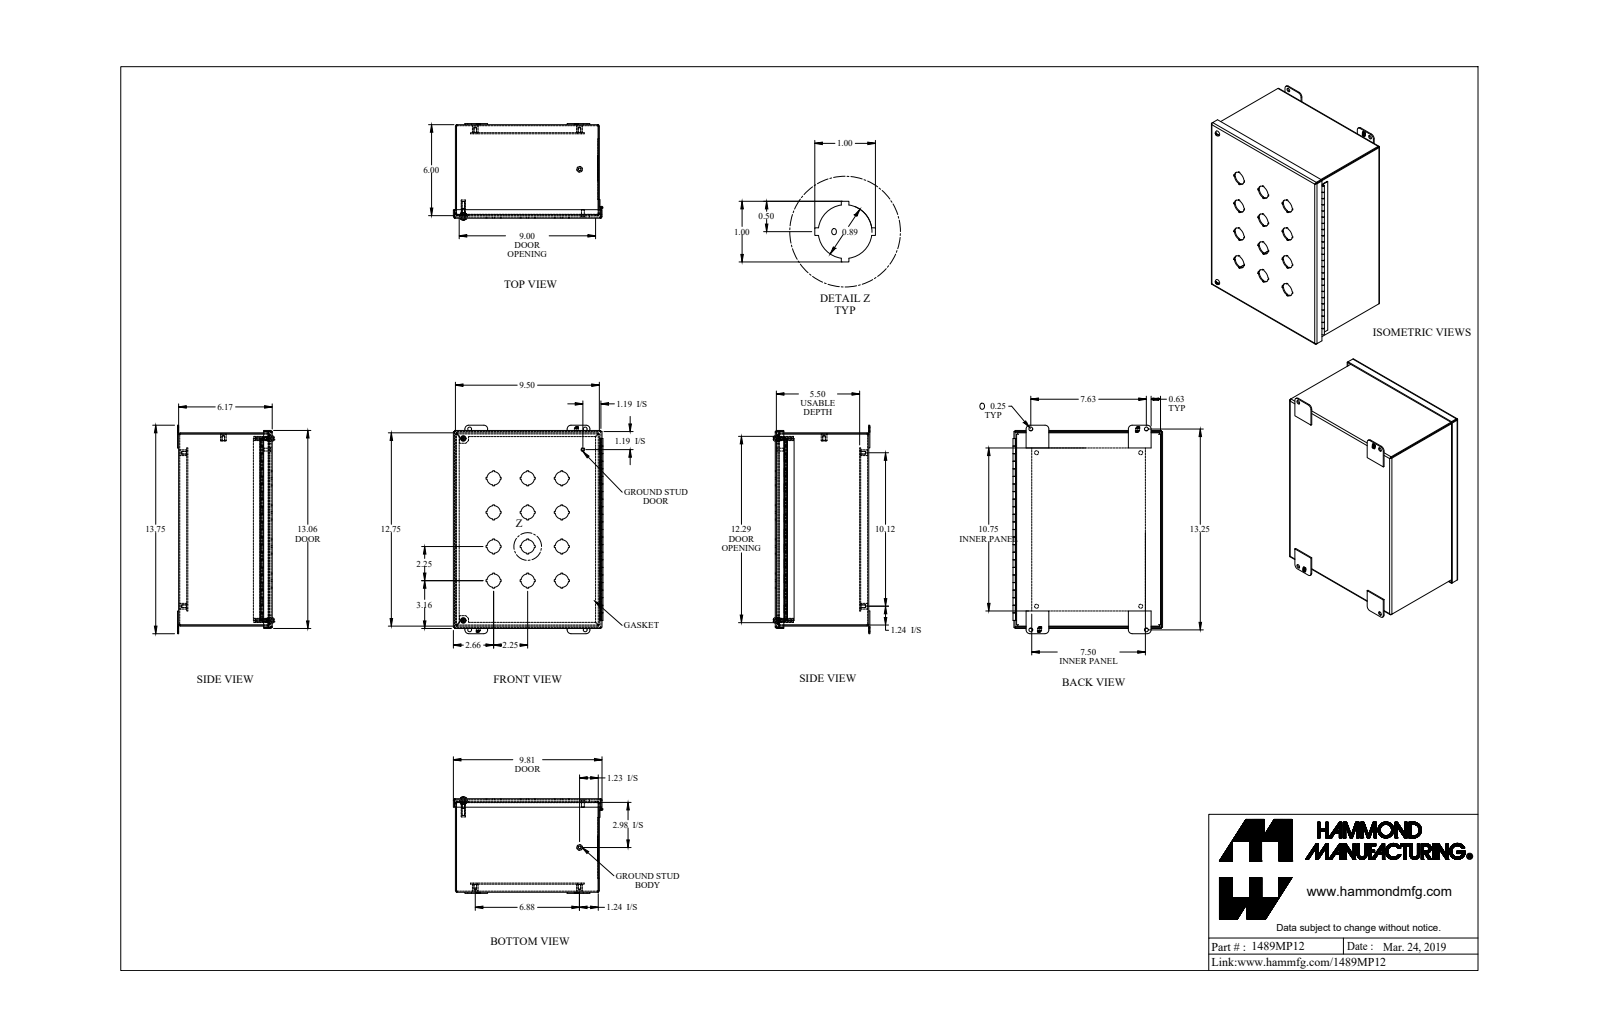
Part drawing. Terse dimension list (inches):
name: 1489MP12_Default
written by: SolidWorks 2019 (CONFIG_CONTROL_DESIGN)
unit: in
bodies: 21 solids, 921 faces (633 planar, 230 cylindrical, 58 other)
size: 13.75 × 9.873 × 6.371
volume: 51.39 in³; area: 1 376 in²
holes: 12× ⌀0.886, 6× ⌀0.25, 5× ⌀0.156, 4× ⌀0.265, 2× ⌀0.159, 2× ⌀0.406
bosses: 5× ⌀0.375, 2× ⌀0.39, 2× ⌀0.275, 2× ⌀0.19, 2× ⌀0.148, 1× ⌀0.25, 1× ⌀0.188, 1× ⌀0.174
rounds: 12× R0.036, 12× R0.108, 8× R0.25, 2× R0.16, 2× R0.171
face distances: 0.072, 6.1, 5.568, 0.532, 9.428, 6.172, 6.028, 12.678, 0.604, 5.64
hole spacings: 2.25, 5.031, 3.182, 4.5, 6.875, 7.417, 12, 1.607
